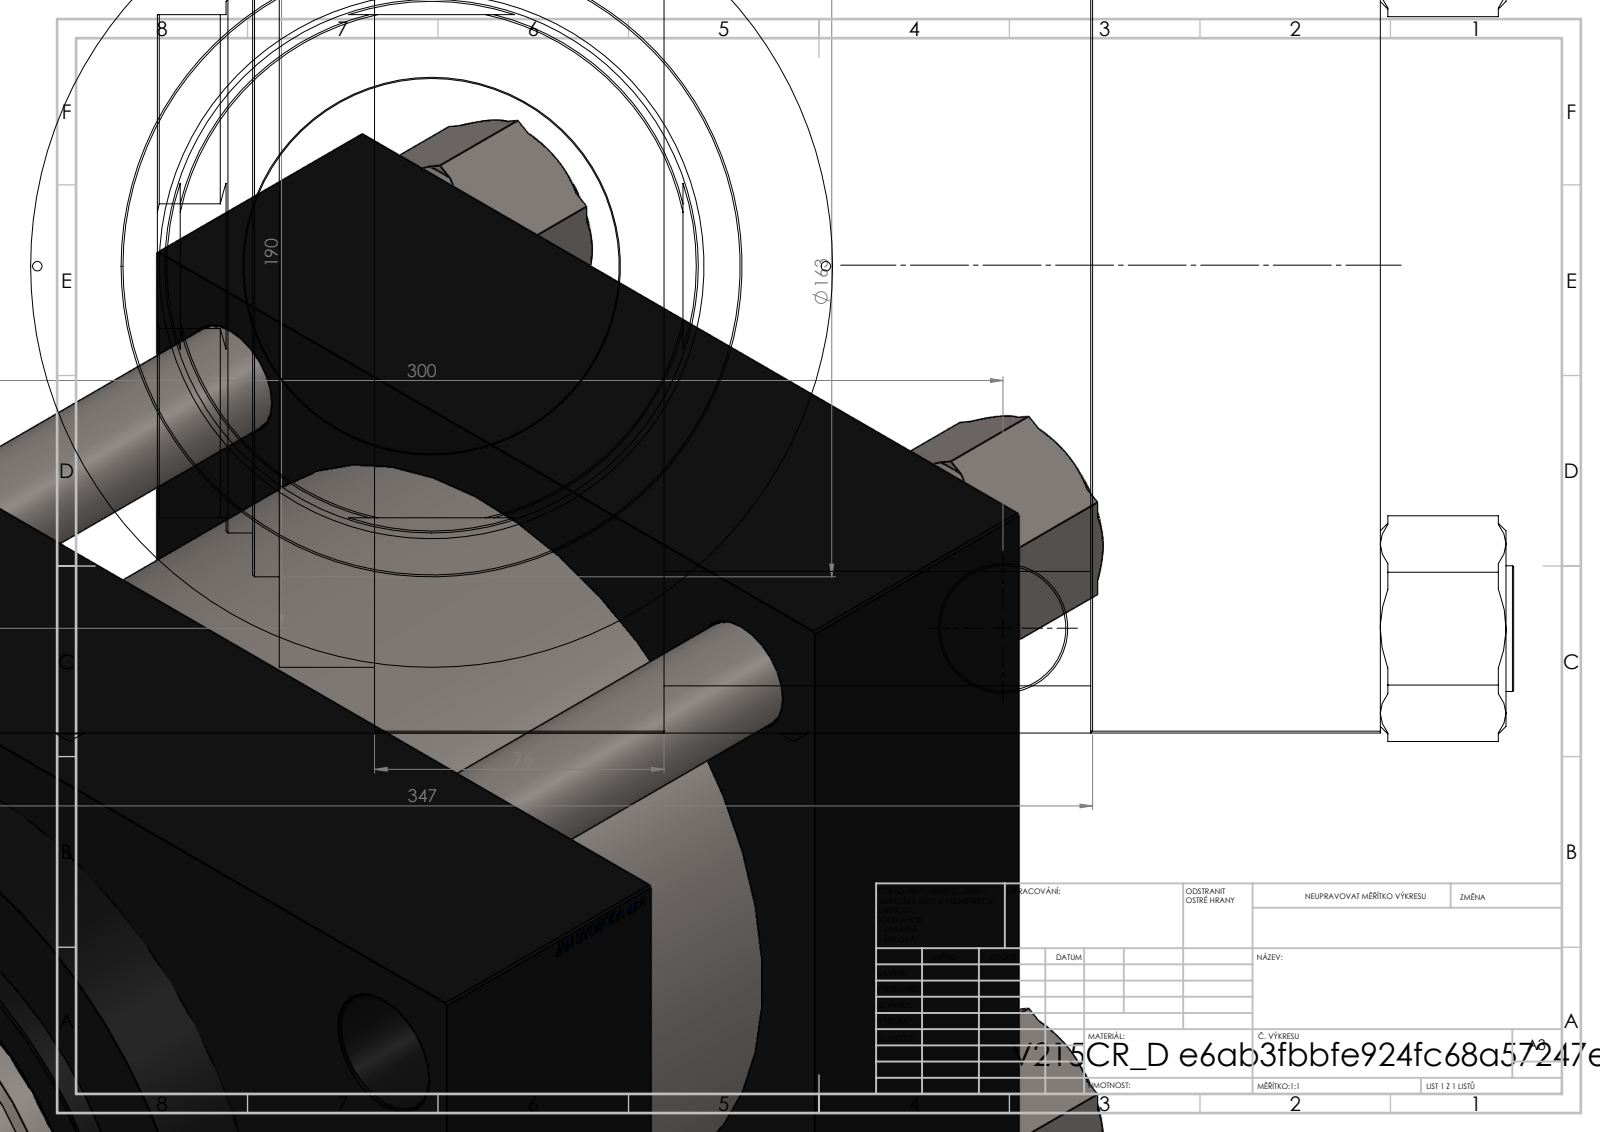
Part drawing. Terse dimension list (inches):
name: NUT_M5_D; V215CR_D_TYCINKA; V215_VC_A; V215CR_VCP_D (+1 more)
written by: SolidWorks 2019 (CONFIG_CONTROL_DESIGN)
unit: in
bodies: 11 solids, 1154 faces (546 planar, 90 cylindrical, 518 other)
size: 14.016 × 13.661 × 9.82
volume: 913.5 in³; area: 1 753 in²
holes: 4× ⌀1.181, 4× ⌀1.299, 2× ⌀0.098, 2× ⌀0.276, 2× ⌀1.65, 2× ⌀2.047, 1× ⌀3.878, 1× ⌀5.512, 1× ⌀5.63, 1× ⌀5.748, 1× ⌀7.874, 1× ⌀8.287
bosses: 4× ⌀1.299, 1× ⌀8.11, 1× ⌀6.417
rounds: 1× R2.677
face distances: 2.992, 7.402, 9.646, 4.409, 10.394, 9.675, 6.683, 2.273, 0.719, 11.654
hole spacings: 2.161, 3.759, 4.164, 5.295, 6.99, 7.488, 7.79, 8.669
